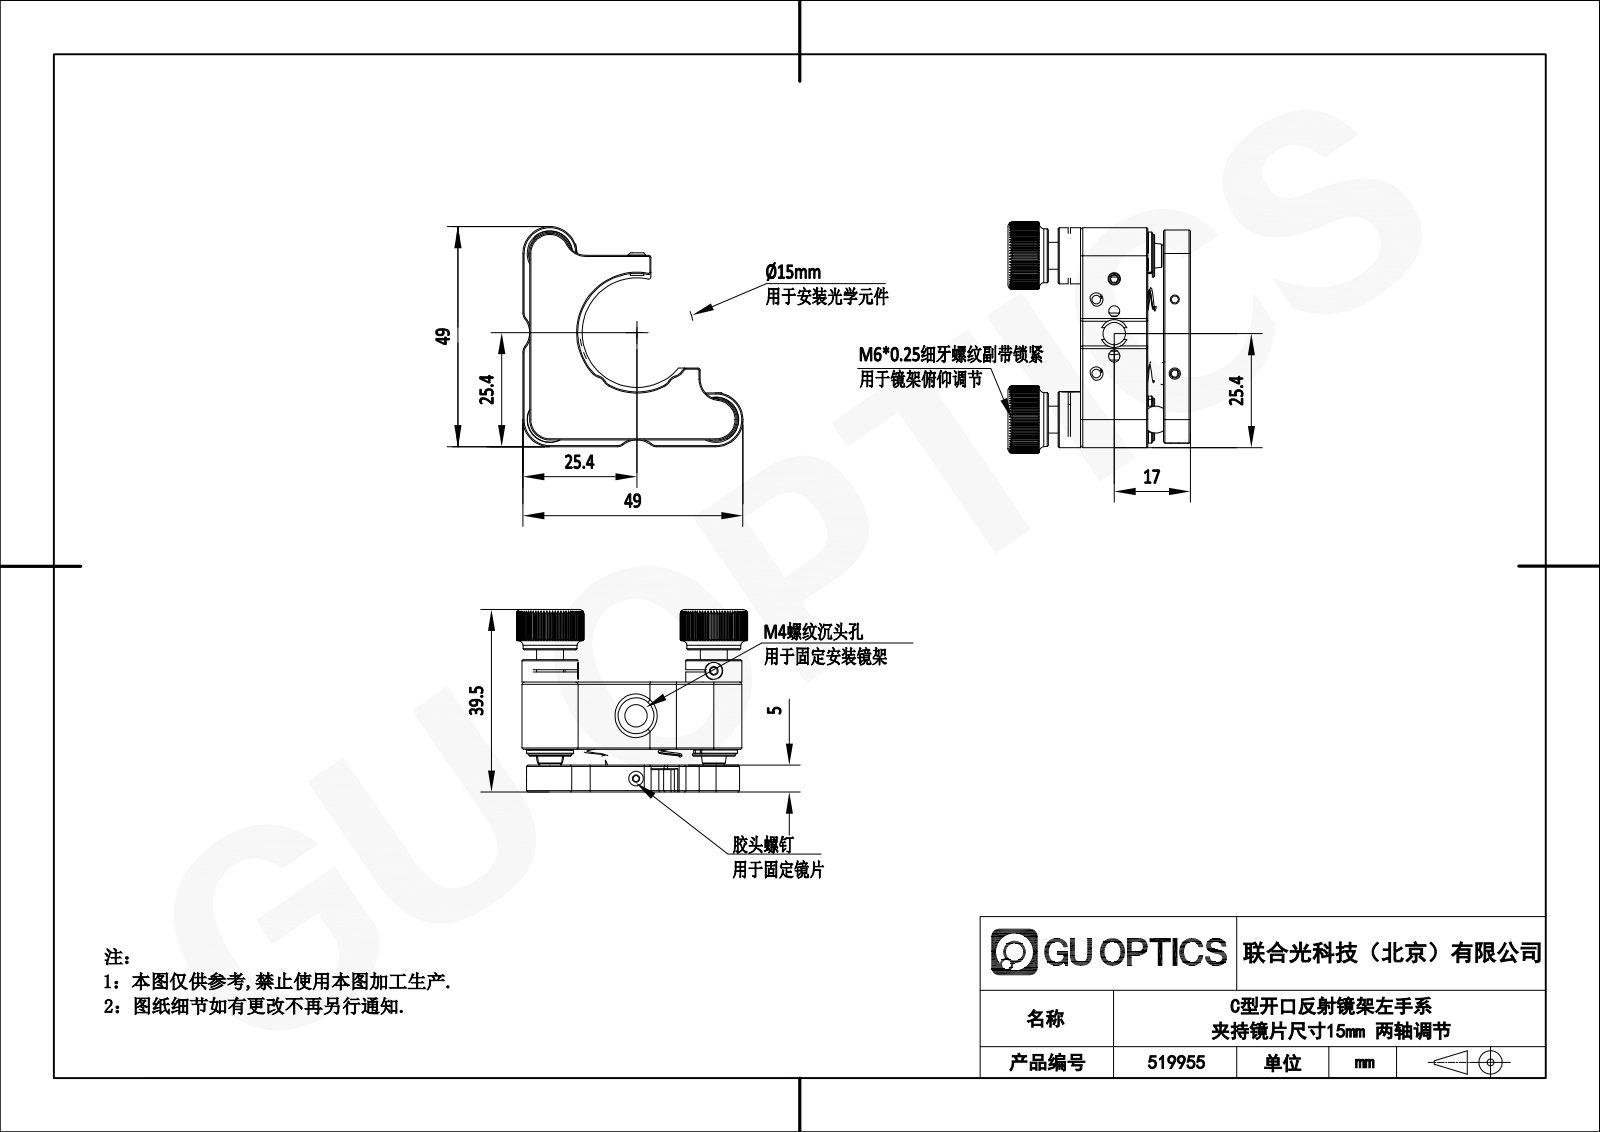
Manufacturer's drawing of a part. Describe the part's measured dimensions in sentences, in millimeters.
The part is named "JC版，2.1.13.17，OMC-15L-2，15mmC型开口反射调整架，左手，2轴". Its 3-D file was written by "SolidWorks 2022 (AUTOMOTIVE_DESIGN)". It is 0 solids with 1031 faces: 463 planar, 332 cylindrical and 236 other. Overall it measures 51.5 by 51.5 by 40.7 millimeters. Round holes: 4 of diameter 2.5, 4 of diameter 6, 2 of diameter 4, 2 of diameter 4.6, 2 of diameter 5, 2 of diameter 8, 1 of diameter 3.3. Round bosses or shafts: 8 of diameter 3, 4 of diameter 1.5, 3 of diameter 4, 2 of diameter 12.5, 2 of diameter 12, 2 of diameter 10.5, 2 of diameter 9.5, 2 of diameter 8. Partial cylindrical surfaces (rounded edges, fillets, slot ends): 8 of radius 0.8, 7 of radius 0.3, 5 of radius 1, 5 of radius 2.5, 4 of radius 0.15, 4 of radius 0.5, 4 of radius 1.25, 4 of radius 1.5. The main face-to-face distances are 6, 24.5, 18.5, 3.5, 9.5, 15, 1, 2.25, 2.75, 11.5. The hole center spacings are 5, 9.75, 16.5, 26.25, 28.65, 37.91, 45.25, 7.2.
